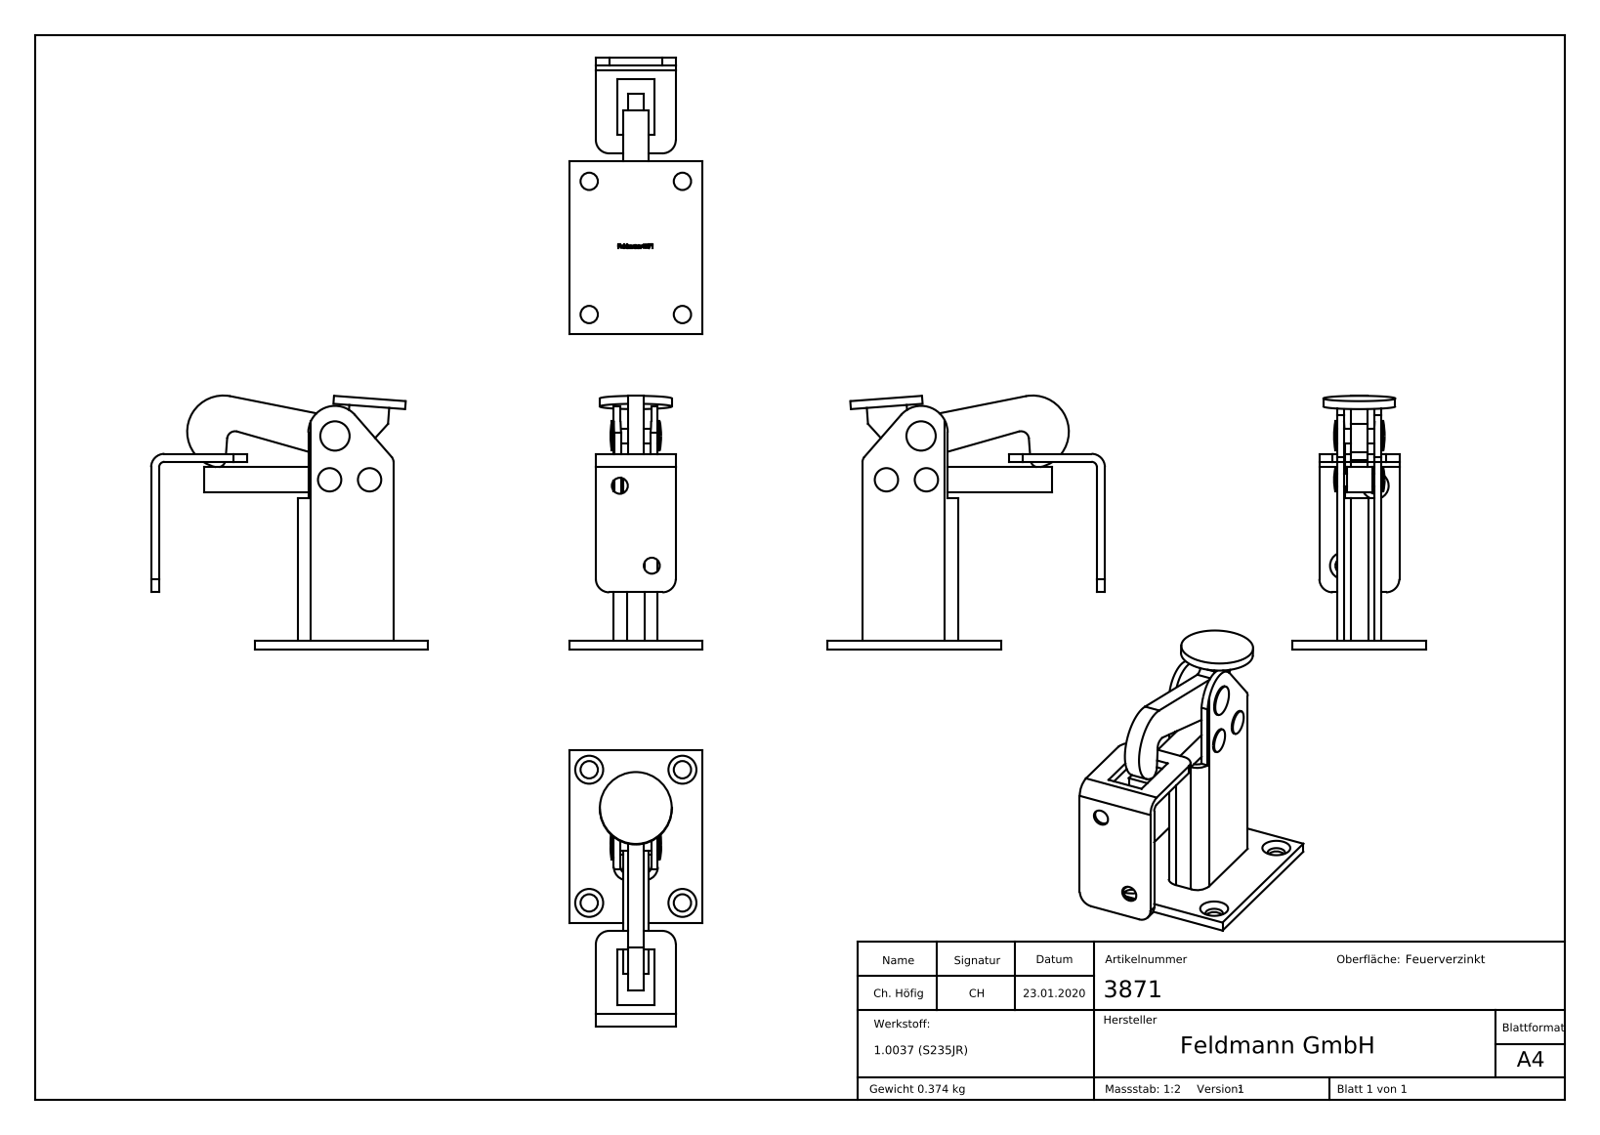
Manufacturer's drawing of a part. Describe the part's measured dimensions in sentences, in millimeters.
The part is named "3871 Teil6; 3871 Teil5; 3871 Teil4_3871 Teil4; 3871 Teil3_3871 Teil3 (+8 more)". Its 3-D file was written by "SolidWorks 2015 (CONFIG_CONTROL_DESIGN)". It is 7 solids with 274 faces: 139 planar, 44 cylindrical and 91 other. Overall it measures 104 by 95.38 by 50 millimeters. Its volume is 47 941 cubic millimeters and its surface area 34 731 square millimeters. Round holes: 4 of diameter 6.5, 3 of diameter 6, 2 of diameter 5, 1 of diameter 5.75. Round bosses or shafts: 2 of diameter 8.75, 2 of diameter 4.75, 1 of diameter 27, 1 of diameter 11, 1 of diameter 5.5. Partial cylindrical surfaces (rounded edges, fillets, slot ends): 7 of radius 5, 3 of radius 3, 2 of radius 2, 2 of radius 2.5, 2 of radius 10, 1 of radius 13.59. The main face-to-face distances are 2.5, 14, 3.5, 11.5, 16.5, 2.75, 3, 5.25, 11.25, 8.75. The hole center spacings are 35, 50, 61.03, 15, 16.57, 20.97, 32.31.
